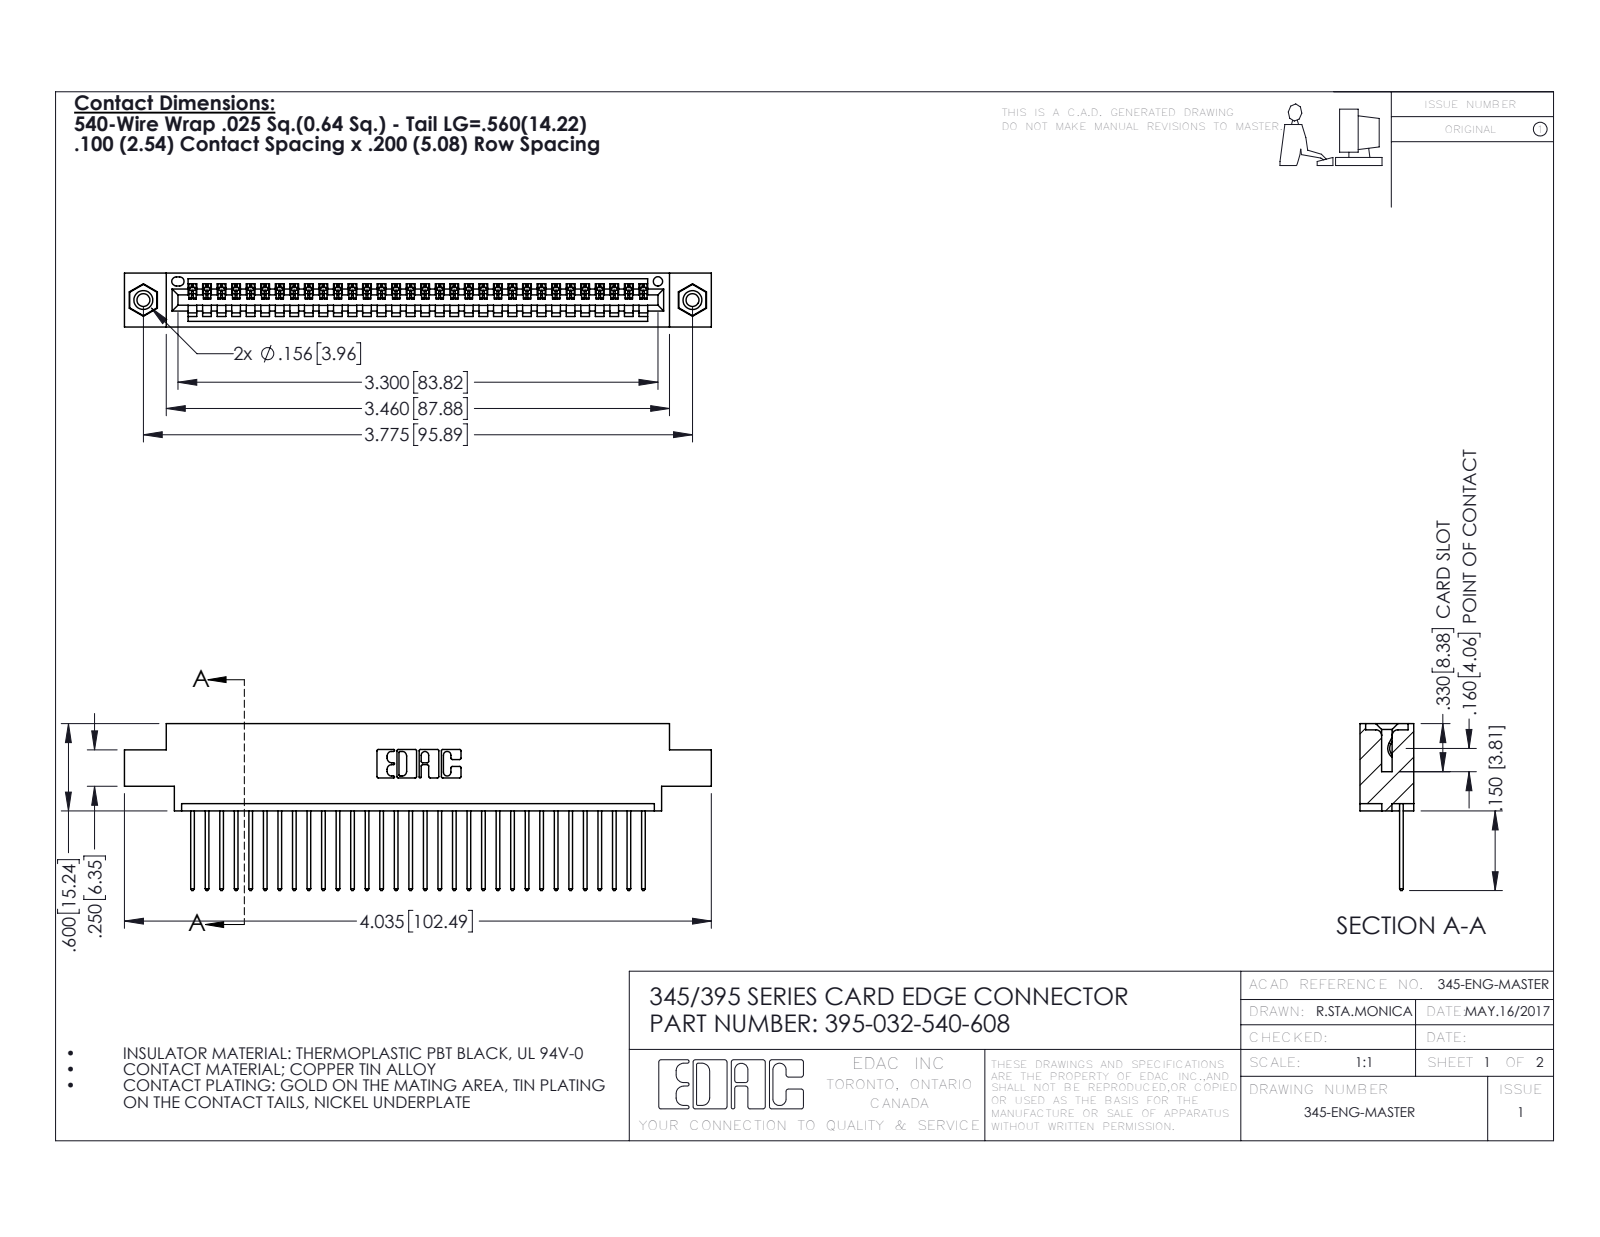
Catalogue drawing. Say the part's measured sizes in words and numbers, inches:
The part is named "395-032-540-608; 345-250-001_345-250-003-102; 345-292-001_345-293-140; 345 Part_0.170 Offset - 0.156 Dia-TI". Its 3-D file was written by "SolidWorks 2016 (CONFIG_CONTROL_DESIGN)". It is 35 solids with 2046 faces: 1396 planar, 634 cylindrical and 16 other. Overall it measures 4.035 by 1.147 by 0.37 inches. Its volume is 0.584 cubic inches and its surface area 20.22 square inches. Round holes: 2 of diameter 0.089, 2 of diameter 0.125, 2 of diameter 0.156, 1 of diameter 0.064. Round bosses or shafts: 2 of diameter 0.155. Partial cylindrical surfaces (rounded edges, fillets, slot ends): 64 of radius 0.006, 64 of radius 0.01, 22 of radius 0.01, 6 of radius 0.007, 6 of radius 0.031, 3 of radius 0.026, 2 of radius 0.031, 2 of radius 0.04. The main face-to-face distances are 0.072, 0.298, 0.37, 0.098, 0.272, 0.025, 0.2, 0.225, 0.175, 0.149. The hole center spacings are 0.27, 3.54, 3.775.
